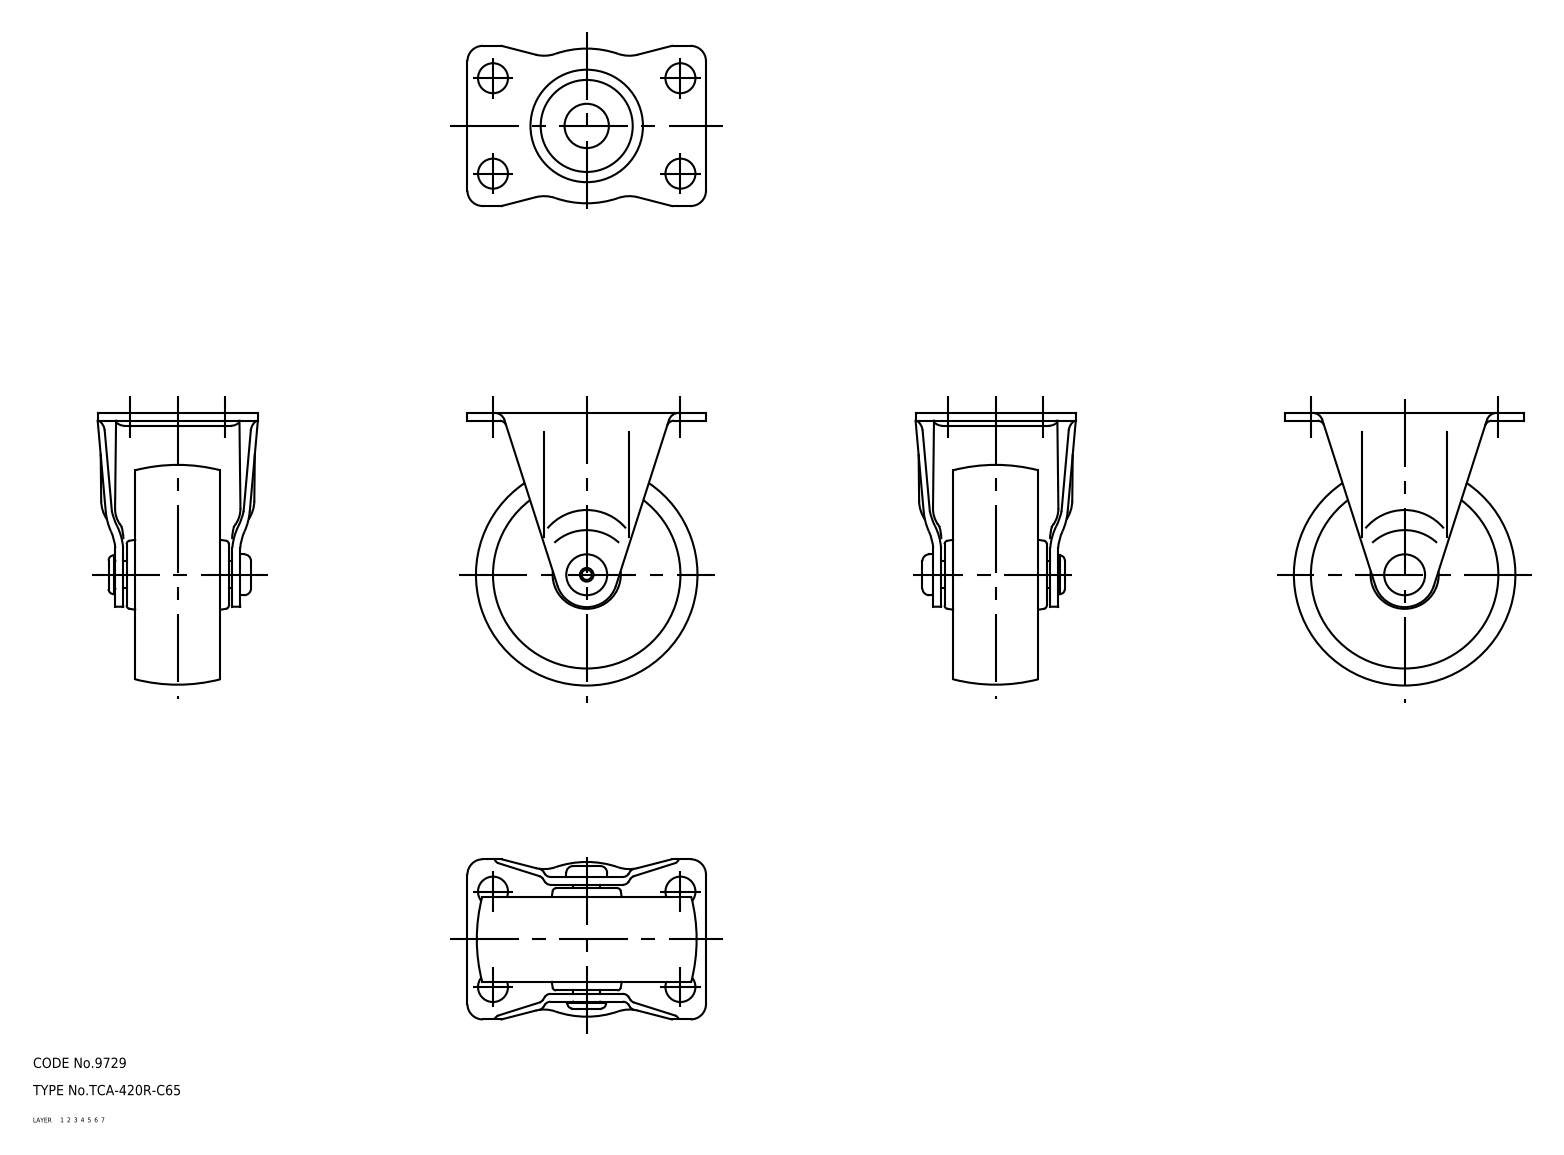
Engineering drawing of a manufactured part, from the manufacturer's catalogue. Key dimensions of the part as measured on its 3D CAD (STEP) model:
Part name (STEP PRODUCT): wheel; axle; No_420_R_C65_5_13168_36
STEP written by: CADfix (AUTOMOTIVE_DESIGN)
Units: millimetres
Bodies: 3 solids, 178 faces (0 planar, 0 cylindrical, 178 other)
Overall size (bounding box): 80 × 70 × 47
Volume: 76 613 mm³ · Surface area: 29 060 mm²
